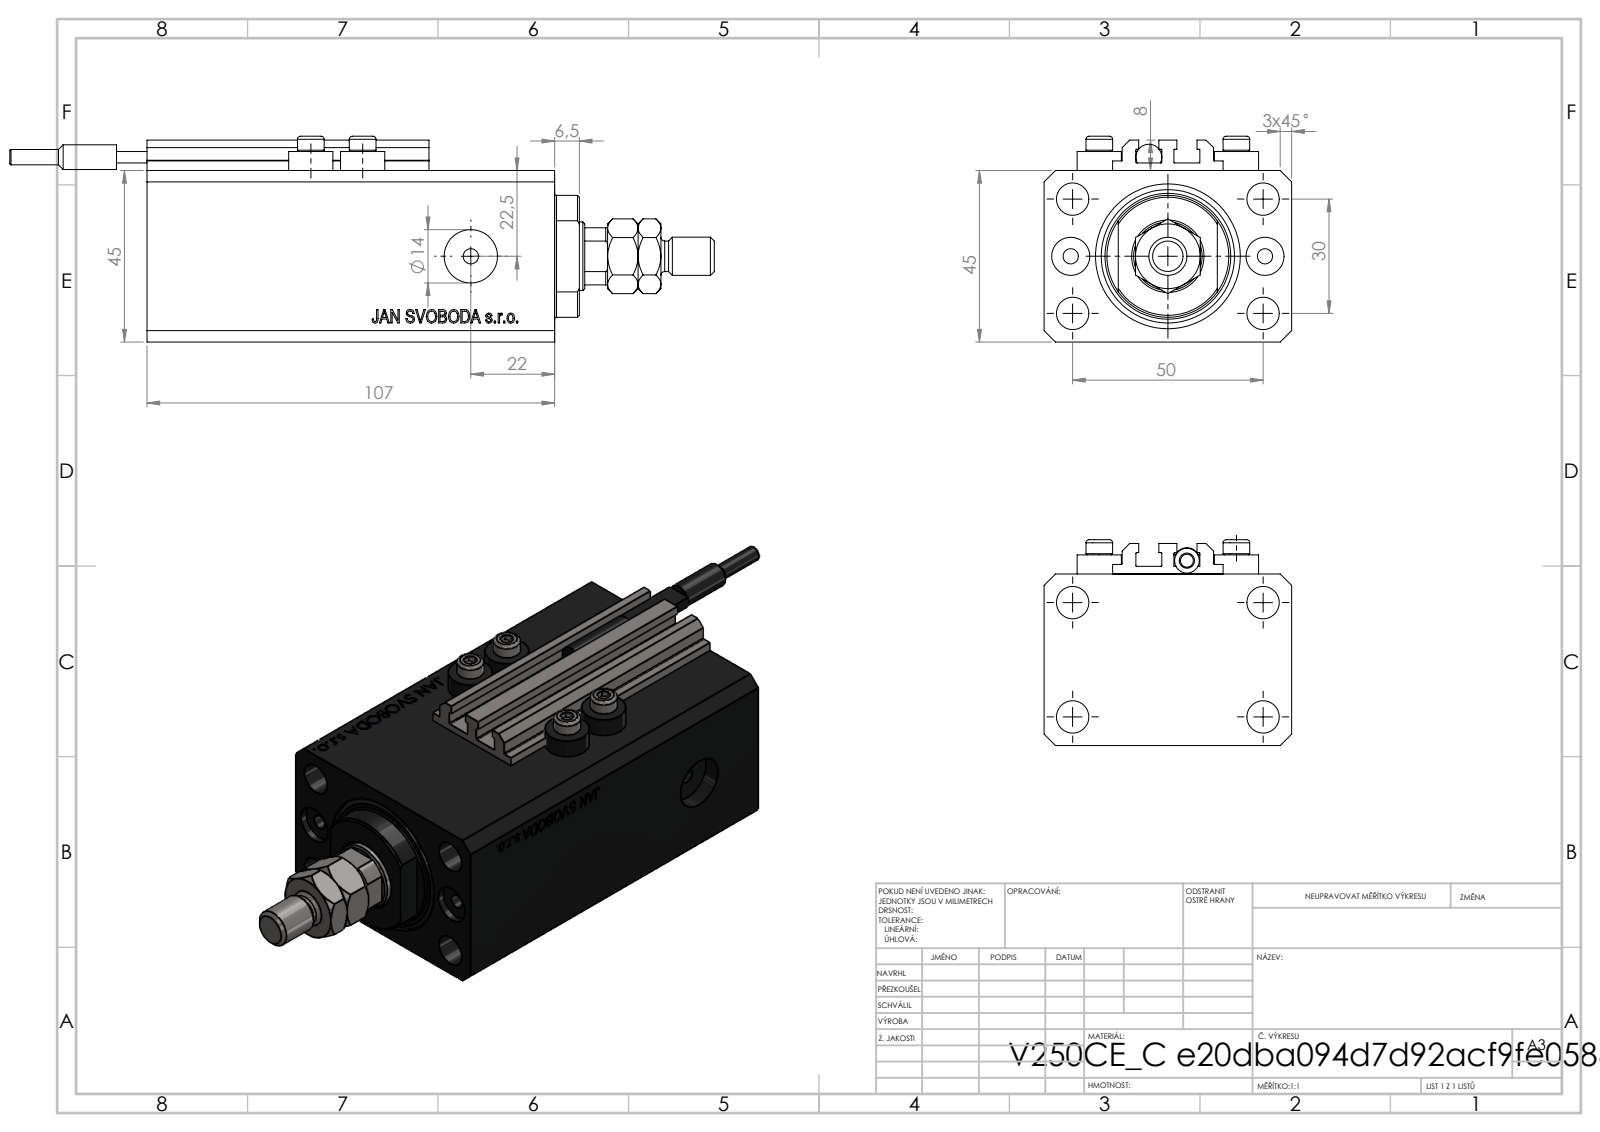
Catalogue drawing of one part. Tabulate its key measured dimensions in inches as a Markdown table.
| quantity | value |
| --- | --- |
| part name | V250CE_C_VCP; V250CE_VC_C; SWITCH_V250CE; ALLEN BOLT V250CE (+2 more) |
| STEP written by | SolidWorks 2019 (CONFIG_CONTROL_DESIGN) |
| units | inches |
| bodies | 10 solids, 1108 faces (534 planar, 96 cylindrical, 478 other) |
| overall size | 7.28 × 2.559 × 2.126 |
| volume | 18.02 in³ |
| surface area | 122.8 in² |
| round holes (diameter × count) | 0.157 × 8, 0.335 × 5, 0.394 × 2, 0.551 × 2, 0.709 × 1, 0.984 × 1, 1.496 × 1 |
| round bosses / shafts (diameter × count) | 0.457 × 4, 0.276 × 4, 0.394 × 1, 0.315 × 1, 0.268 × 1, 0.256 × 1, 0.157 × 1 |
| partial cylindrical surfaces (radius × count) | 0.008 × 10, 0.335 × 1, 0.63 × 1 |
| main face-to-face distances | 1.772, 2.559, 0.988, 3.224, 4.213, 1.85, 0.118, 0.272, 0.079, 0.098 |
| hole center spacings | 0.591, 1.148, 2.074, 0.535, 1.004, 1.181, 1.417, 1.515 |
